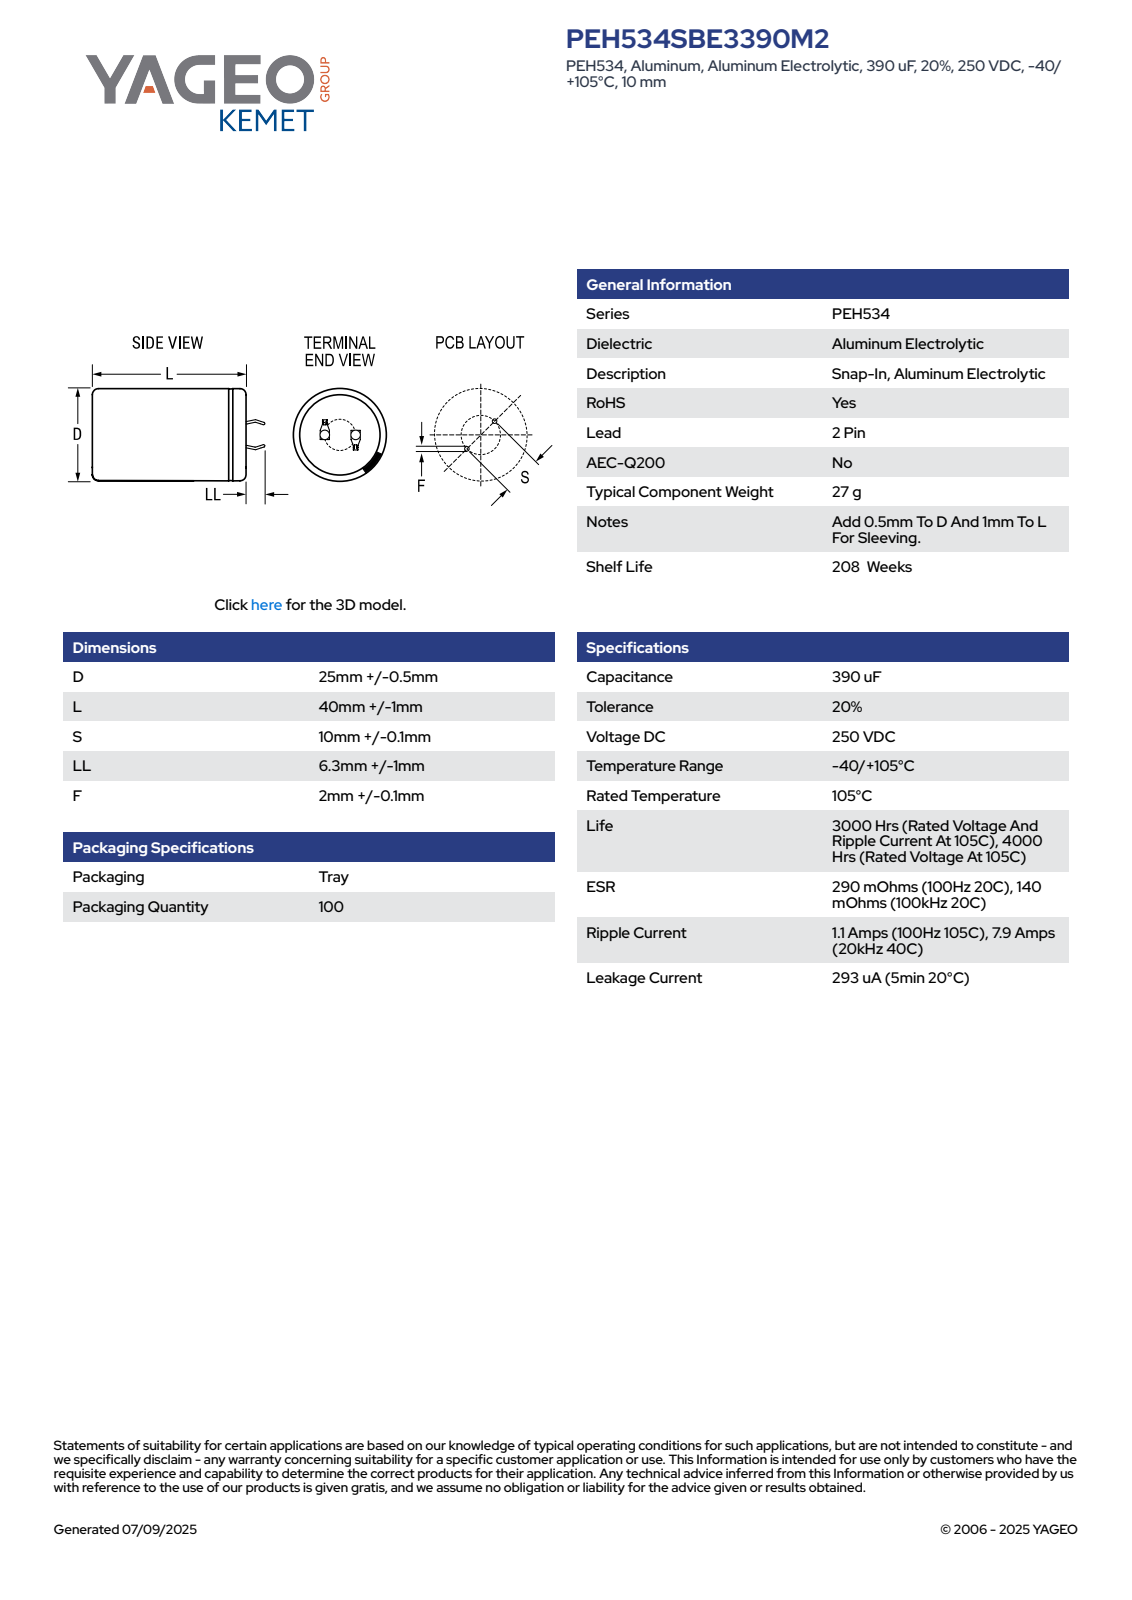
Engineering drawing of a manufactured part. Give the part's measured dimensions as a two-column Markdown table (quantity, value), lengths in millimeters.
| quantity | value |
| --- | --- |
| part name | CARS_K2P_25X40_D25.5L41S10LL7.3F2.1 |
| STEP written by | SolidWorks 2014 (AUTOMOTIVE_DESIGN) |
| units | millimeters |
| bodies | 1 solid, 100 faces (52 planar, 9 cylindrical, 39 other) |
| overall size | 48.29 × 25.5 × 25.5 |
| volume | 20 758 mm³ |
| surface area | 4 328 mm² |
| round holes (diameter × count) | 22.56 × 1 |
| round bosses / shafts (diameter × count) | 25.5 × 1 |
| partial cylindrical surfaces (radius × count) | 12.74 × 1 |
| main face-to-face distances | 40.99, 0.6, 41.49, 0.5, 7.08, 7.64, 0.75, 1.35, 7.68, 6.48 |
